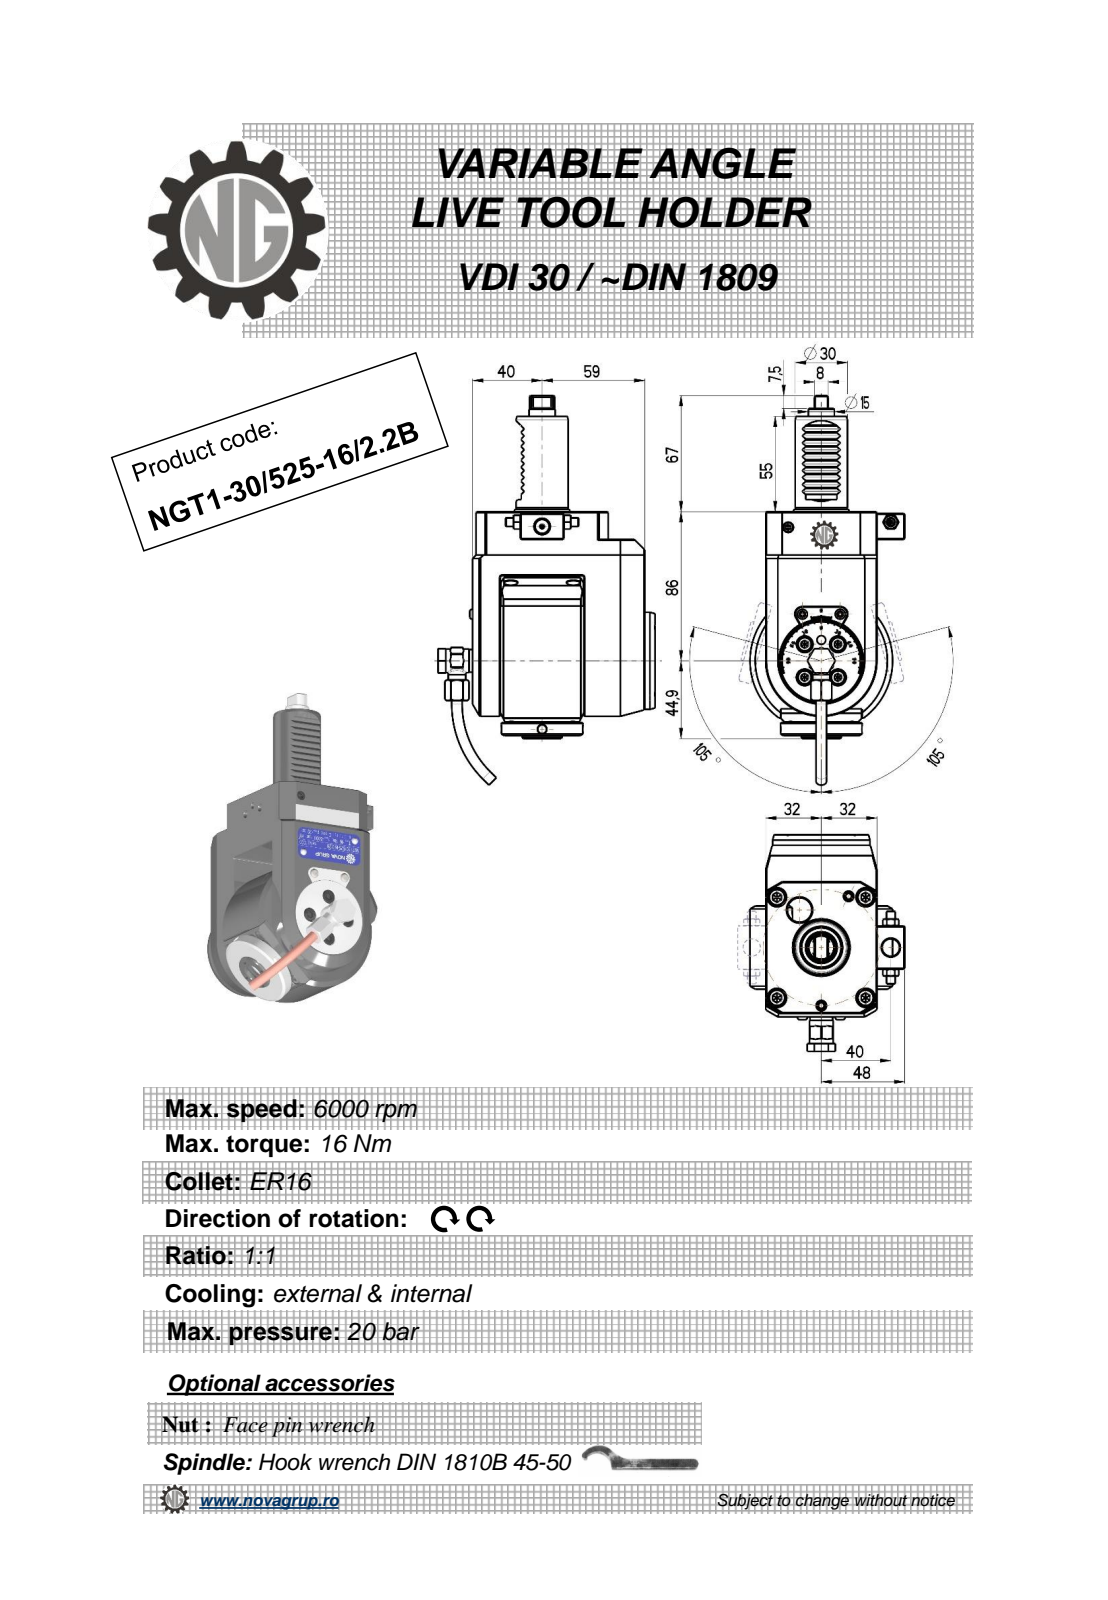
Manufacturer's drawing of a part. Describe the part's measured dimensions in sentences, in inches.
The part is named "NGT1_30_521_16_2_2B". Its 3-D file was written by "PRO/ENGINEER BY PARAMETRIC TECHNOLOGY CORPORATION, 2010280 (CONFIG_CONTROL_DESIGN)". It is 1 solid with 510 faces: 218 planar, 140 cylindrical and 152 other. Overall it measures 8.845 by 4.917 by 3.504 inches. Its volume is 47.41 cubic inches and its surface area 110.8 square inches. Round holes: 4 of diameter 0.126, 3 of diameter 0.157, 2 of diameter 0.197, 1 of diameter 0.118, 1 of diameter 0.165, 1 of diameter 0.244, 1 of diameter 0.354, 1 of diameter 0.374, 1 of diameter 0.394, 1 of diameter 0.433, 1 of diameter 0.492. Round bosses or shafts: 2 of diameter 0.394, 2 of diameter 0.236, 2 of diameter 0.224, 1 of diameter 2.205, 1 of diameter 1.85, 1 of diameter 1.378, 1 of diameter 1.181, 1 of diameter 0.906. Partial cylindrical surfaces (rounded edges, fillets, slot ends): 12 of radius 0.01, 10 of radius 0.012, 6 of radius 0.006, 4 of radius 0.02, 2 of radius 0.031, 2 of radius 0.039, 1 of radius 0.283, 1 of radius 0.303. The main face-to-face distances are 2.52, 0.63, 1.457, 3.898, 0.236, 4.134, 0.827, 0.551, 2.441, 3.268. The hole center spacings are 0.364, 0.515, 0.728, 1.617, 1.963, 1.979, 0.016, 1.211.
